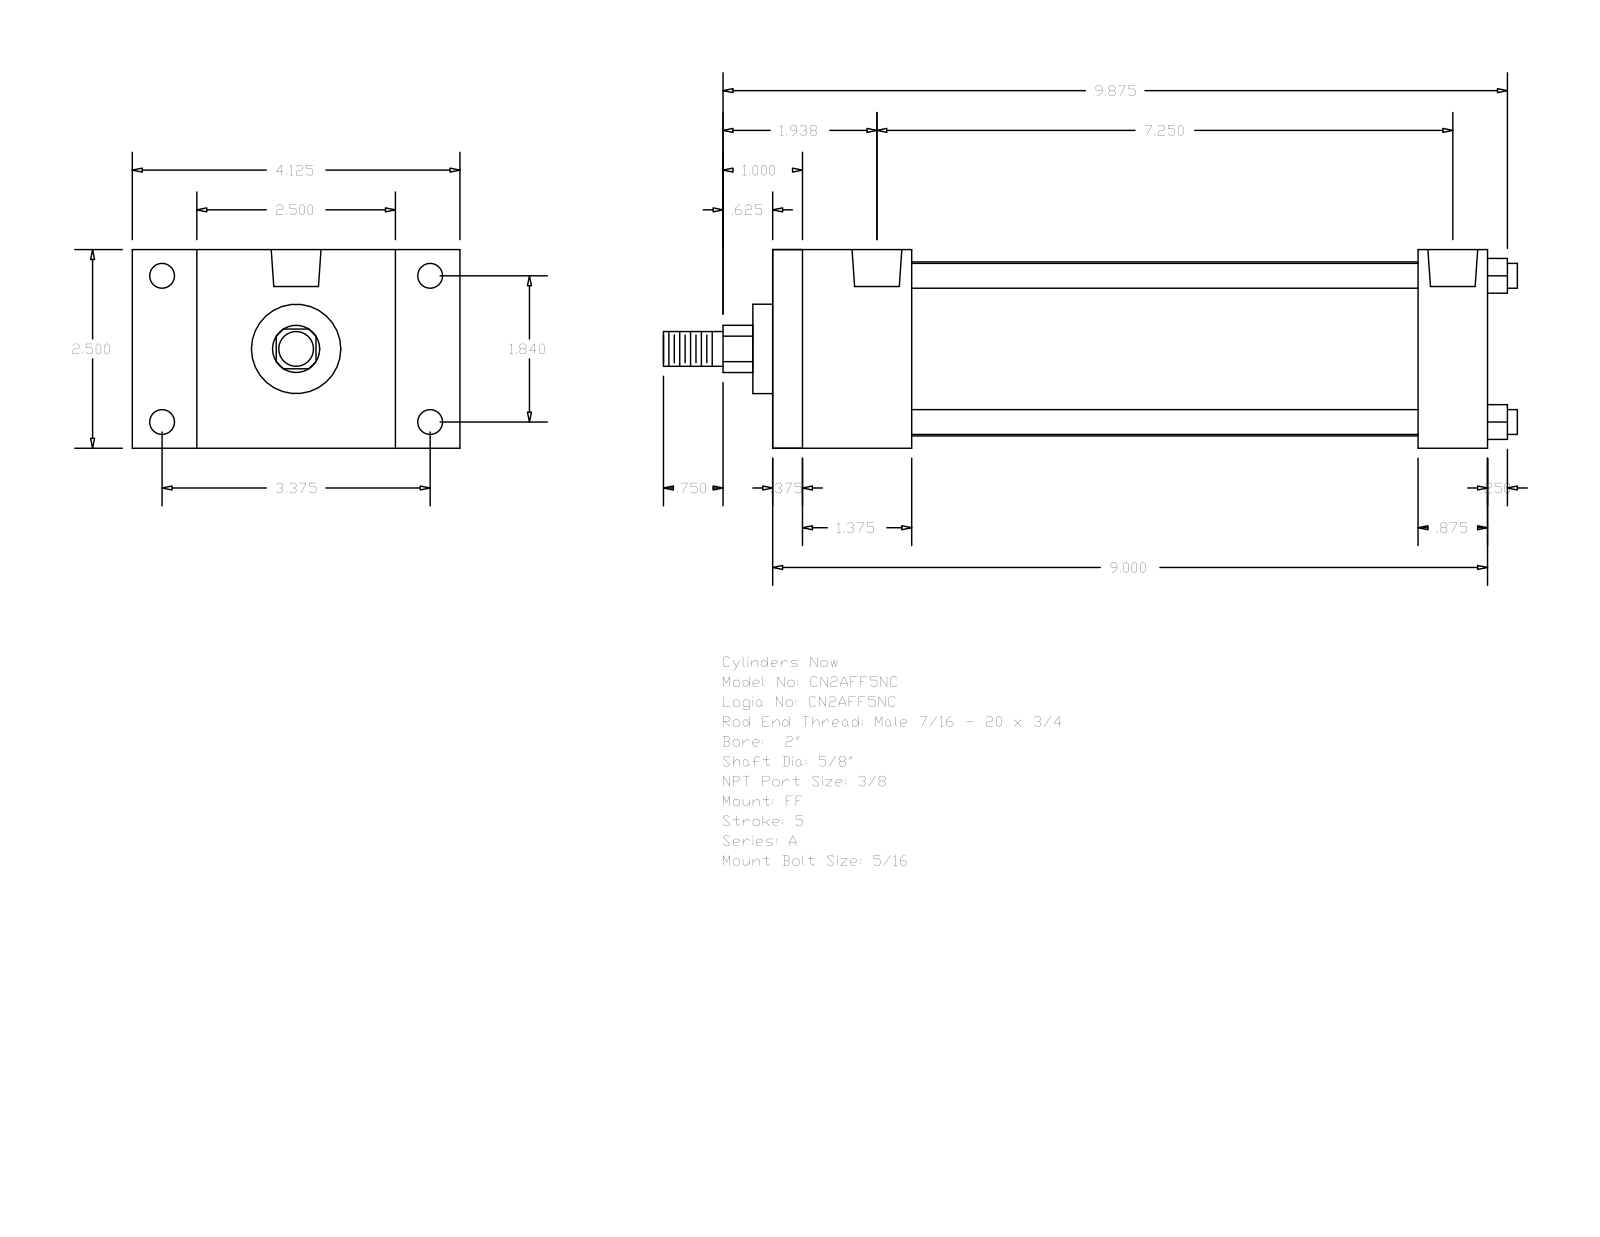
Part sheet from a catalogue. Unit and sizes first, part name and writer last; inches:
Units: inches
Overall size (bounding box): 10.75 × 4.125 × 2.5
Round holes (diameter × count): ⌀0.219 ×4, ⌀0.313 ×4, ⌀0.627 ×2
Round bosses / shafts (diameter × count): ⌀0.313 ×4, ⌀2.19 ×1, ⌀1.125 ×1, ⌀0.625 ×1, ⌀0.437 ×1
Partial cylindrical surfaces — rounded edges, fillets, slot ends (radius × count): R0.297 ×1
Main face-to-face distances: 2.5, 9, 0.375, 8.625, 1.375, 1.75, 8.125, 7.75, 6.375, 7.25
Hole centre spacings: 1.84, 3.375, 3.844, 6.937, 0.156, 0.157, 7.093, 7.094
Bodies: 0 solids, 92 faces (64 planar, 28 cylindrical, 0 other)
Part name (STEP PRODUCT): A_FF__0200_0.625
STEP written by: GSSL Pune (CONFIG_CONTROL_DESIGN)
